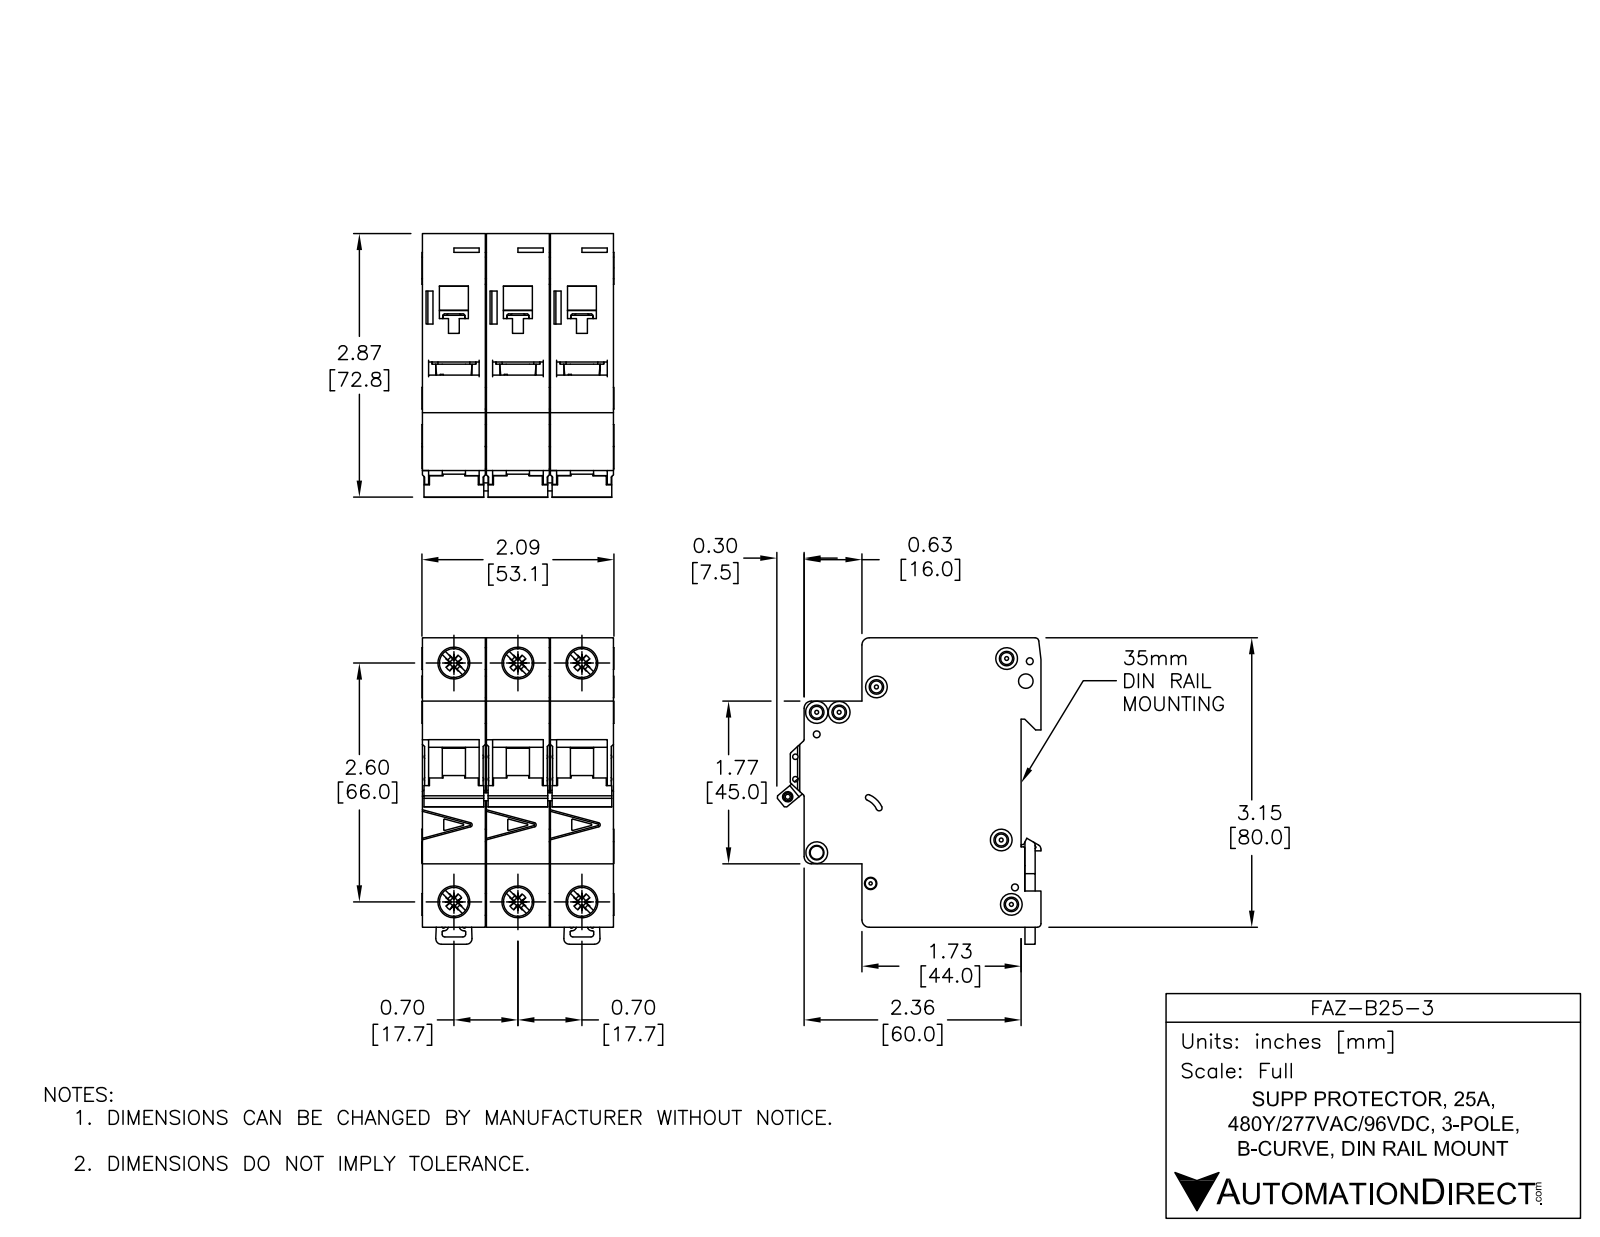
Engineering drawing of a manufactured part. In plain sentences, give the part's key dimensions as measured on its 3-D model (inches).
The part is named "FAZ-B25-3". Its 3-D file was written by "SolidWorks 2014 (AUTOMOTIVE_DESIGN)". It is 11 solids with 1650 faces: 697 planar, 590 cylindrical and 363 other. Overall it measures 3.338 by 2.876 by 2.091 inches. Its volume is 13.71 cubic inches and its surface area 89.98 square inches. Round holes: 6 of diameter 0.142, 4 of diameter 0.323, 3 of diameter 0.075, 2 of diameter 0.043, 2 of diameter 0.059, 2 of diameter 0.157, 2 of diameter 0.281, 1 of diameter 0.085, 1 of diameter 0.087, 1 of diameter 0.1, 1 of diameter 0.13, 1 of diameter 0.134. Round bosses or shafts: 4 of diameter 0.236, 3 of diameter 0.098, 2 of diameter 0.323. Partial cylindrical surfaces (rounded edges, fillets, slot ends): 68 of radius 0.01, 25 of radius 0.02, 12 of radius 0.039, 12 of radius 0.079, 11 of radius 0.008, 3 of radius 0.071, 2 of radius 0.031, 2 of radius 0.118. The main face-to-face distances are 0.697, 0.689, 1.394, 1.386, 2.083, 0.705, 3.129, 0.217, 1.949, 1.732. The hole center spacings are 0.697, 2.69, 2.598, 0.244, 0.537, 1.394, 2.948, 0.189.
